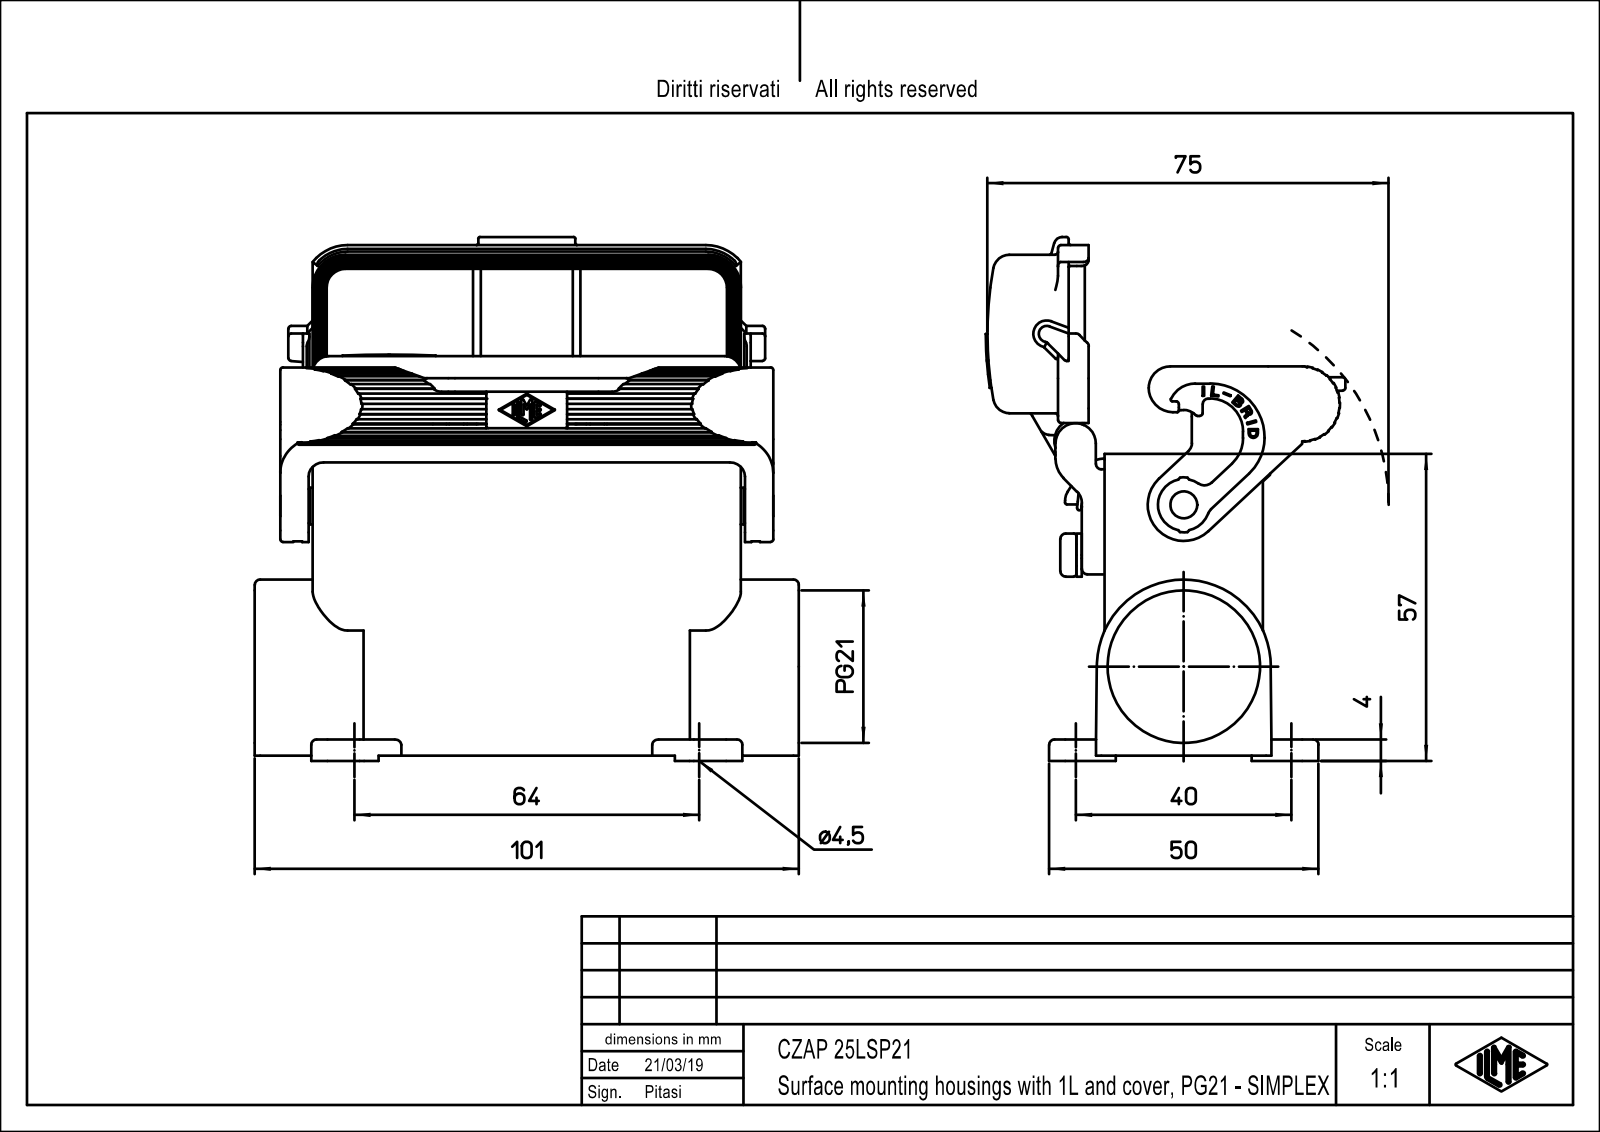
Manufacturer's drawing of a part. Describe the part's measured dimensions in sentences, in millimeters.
The part is named "CZAP_25_LSP21". Its 3-D file was written by "PTC Creo Elements/Direct Modeling 19.0E 27-Jun-2016 (C) Parametric Technology GmbH (AUTOMOTIVE_DESIGN)". It is 1 solid with 537 faces: 293 planar, 214 cylindrical and 30 other. Overall it measures 101 by 97.03 by 66.47 millimeters. Its volume is 86 501 cubic millimeters and its surface area 55 888 square millimeters. Round holes: 4 of diameter 3, 4 of diameter 4.5, 1 of diameter 23.5, 1 of diameter 28.3. Round bosses or shafts: 3 of diameter 0.8, 1 of diameter 8.4, 1 of diameter 8, 1 of diameter 6.8, 1 of diameter 4.8, 1 of diameter 2.4. Partial cylindrical surfaces (rounded edges, fillets, slot ends): 13 of radius 3, 12 of radius 3.5, 7 of radius 0.5, 7 of radius 6.5, 4 of radius 1.5, 4 of radius 2, 4 of radius 3.2, 4 of radius 3.4. The main face-to-face distances are 2.76, 29.4, 26.65, 23.89, 2.75, 3, 26.64, 2.6, 26.8, 3.8. The hole center spacings are 12.04, 28.02, 66.1, 70.77, 16, 40, 64, 66.
